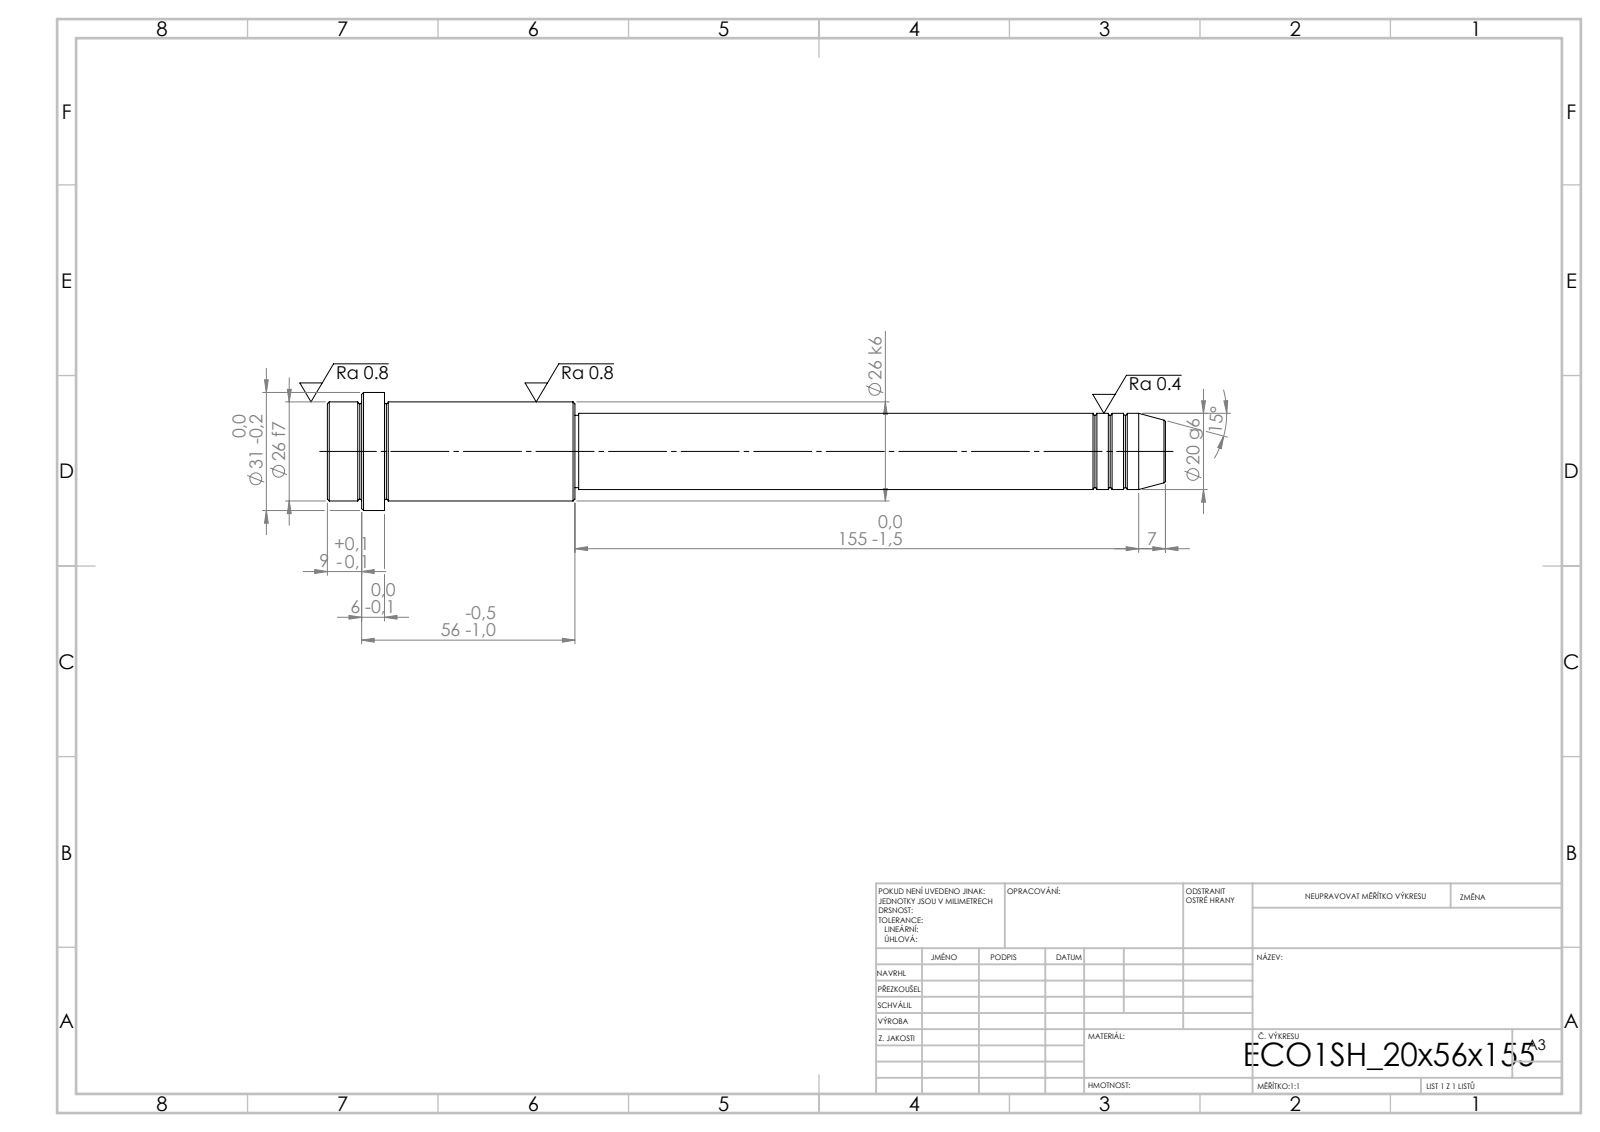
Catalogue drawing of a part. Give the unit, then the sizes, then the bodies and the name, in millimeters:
Units: millimetres
Overall size (bounding box): 220 × 31 × 31
Round bosses / shafts (diameter × count): ⌀31 ×1, ⌀26 ×1, ⌀20 ×1, ⌀19 ×1
Main face-to-face distances: 15, 50, 65, 155, 205, 220, 211, 56, 6, 9
Volume: 83 962 mm³ · Surface area: 16 678 mm²
Bodies: 1 solid, 52 faces (6 planar, 16 cylindrical, 30 other)
STEP written by: SolidWorks 2019 (CONFIG_CONTROL_DESIGN)
